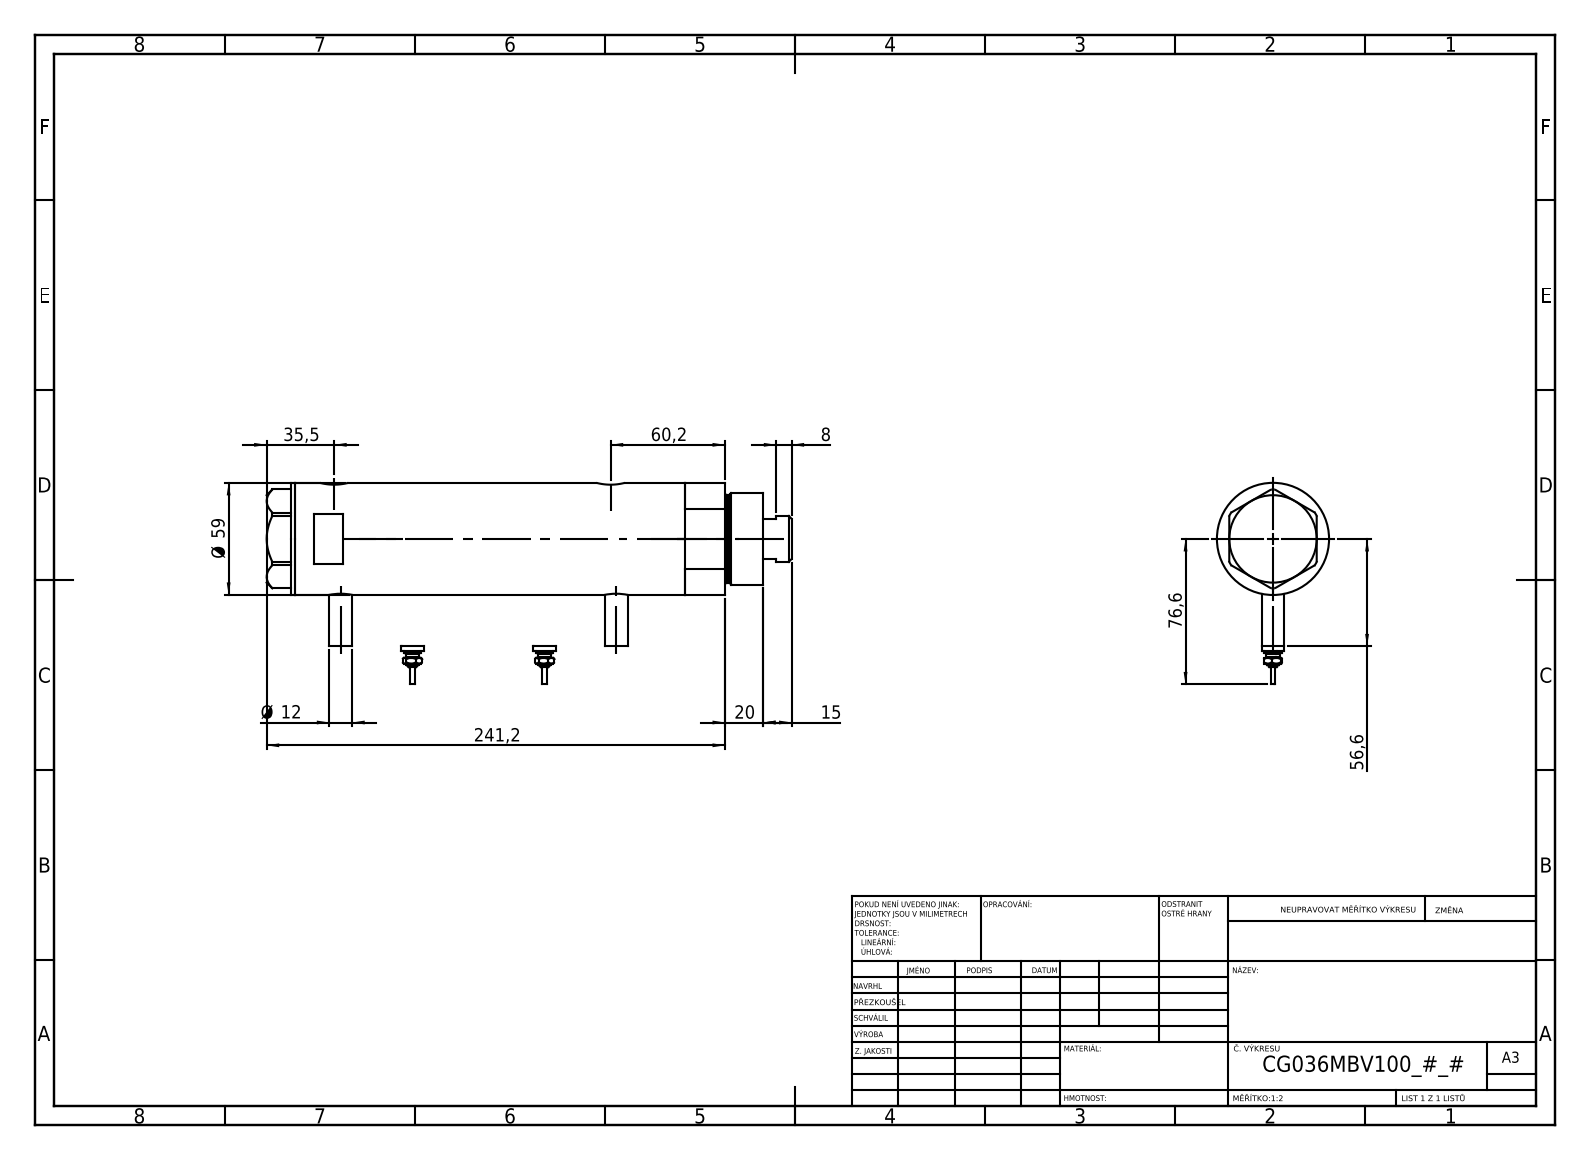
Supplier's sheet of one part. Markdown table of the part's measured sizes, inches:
| quantity | value |
| --- | --- |
| part name | V270CG_BACK; V270CG_VC; V270CG_MIDDLE; Switch (+1 more) |
| STEP written by | SolidWorks 2019 (CONFIG_CONTROL_DESIGN) |
| units | inches |
| bodies | 6 solids, 212 faces (79 planar, 69 cylindrical, 64 other) |
| overall size | 10.874 × 4.177 × 2.323 |
| volume | 38.8 in³ |
| surface area | 198.1 in² |
| round holes (diameter × count) | 0.383 × 2, 0.492 × 2, 0.591 × 2, 0.335 × 1, 0.984 × 1, 1.043 × 1, 1.417 × 1, 1.575 × 1, 2.047 × 1 |
| round bosses / shafts (diameter × count) | 0.472 × 4, 0.354 × 2, 0.276 × 2, 0.177 × 2, 0.098 × 2, 2.323 × 1, 1.89 × 1, 1.811 × 1 |
| main face-to-face distances | 6.583, 0.925, 5.657, 0.591, 1.516, 7.173, 0.079, 10.283, 9.693, 8.768 |
| hole center spacings | 0.114, 0.138, 5.591, 5.705, 5.728, 5.843 |
